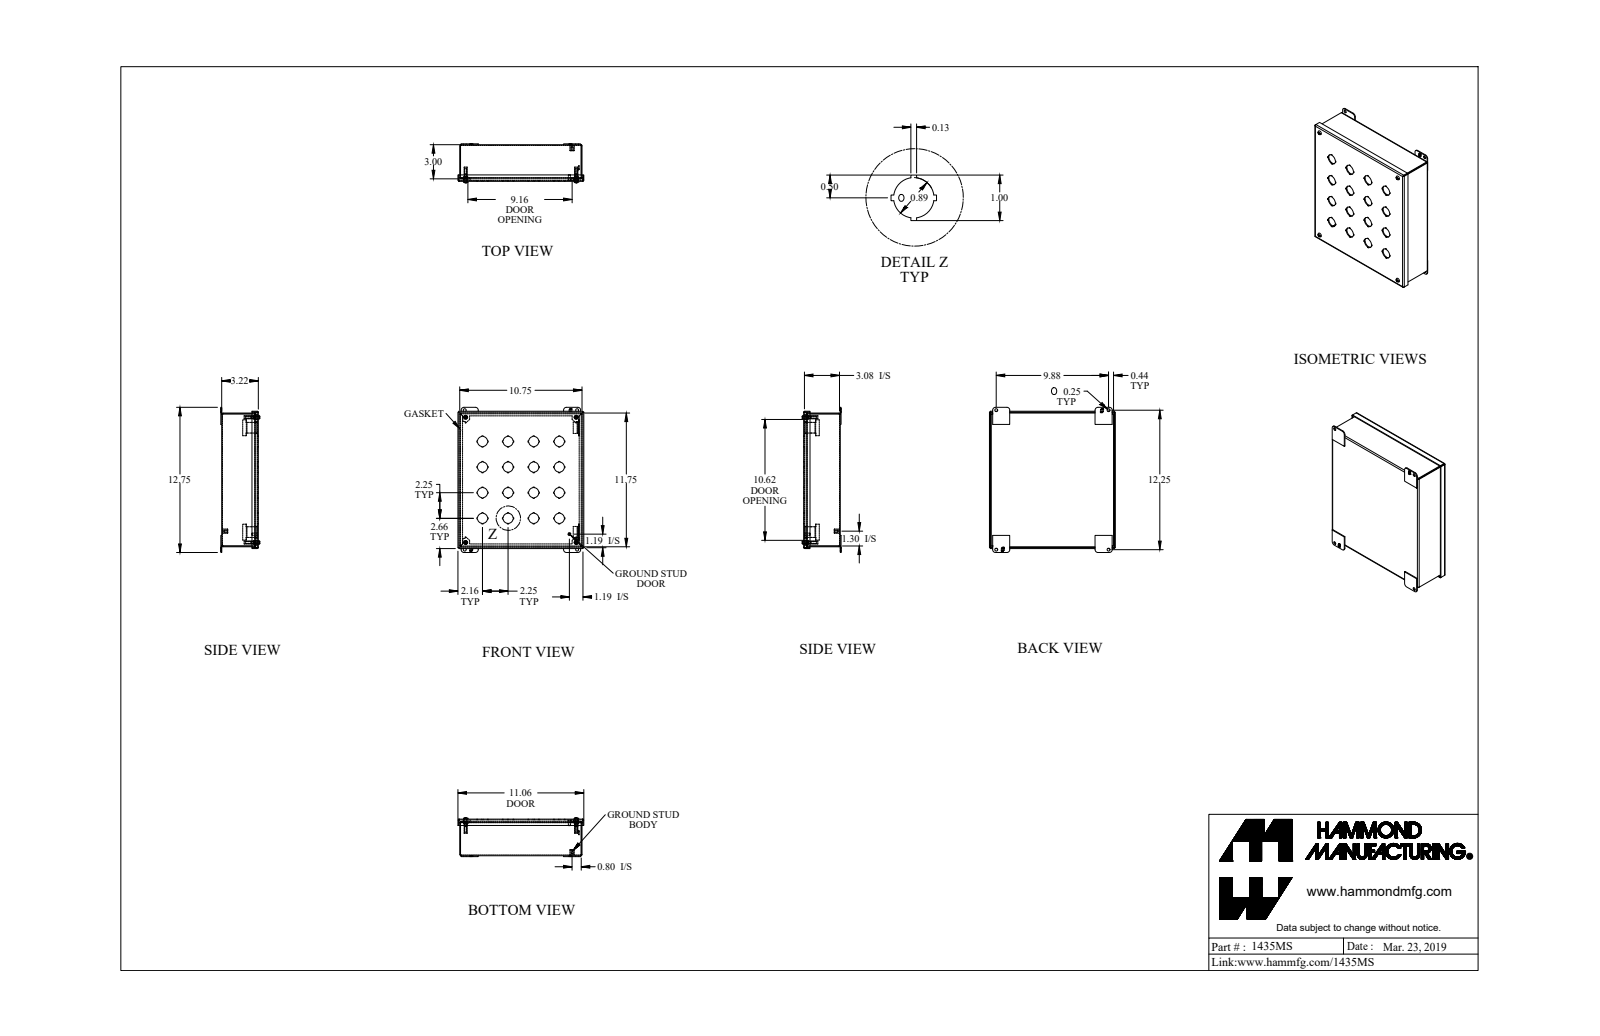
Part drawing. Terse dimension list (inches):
name: 1435MS_Default
written by: SolidWorks 2019 (CONFIG_CONTROL_DESIGN)
unit: in
bodies: 22 solids, 938 faces (674 planar, 212 cylindrical, 52 other)
size: 12.75 × 11.062 × 3.421
volume: 34.63 in³; area: 920 in²
holes: 16× ⌀0.886, 8× ⌀0.25, 4× ⌀0.406, 3× ⌀0.159, 1× ⌀0.156
bosses: 4× ⌀0.19, 4× ⌀0.148, 3× ⌀0.39, 3× ⌀0.275, 1× ⌀0.375, 1× ⌀0.25, 1× ⌀0.188
rounds: 12× R0.036, 12× R0.108, 8× R0.25, 4× R0.029, 4× R0.086, 4× R0.171, 3× R0.16
face distances: 0.072, 3.15, 3.222, 3.078, 10.678, 0.072, 11.678, 10.606, 10.75, 0.156
hole spacings: 2.25, 5.031, 3.182, 4.5, 7.115, 11, 11.626, 6.364
